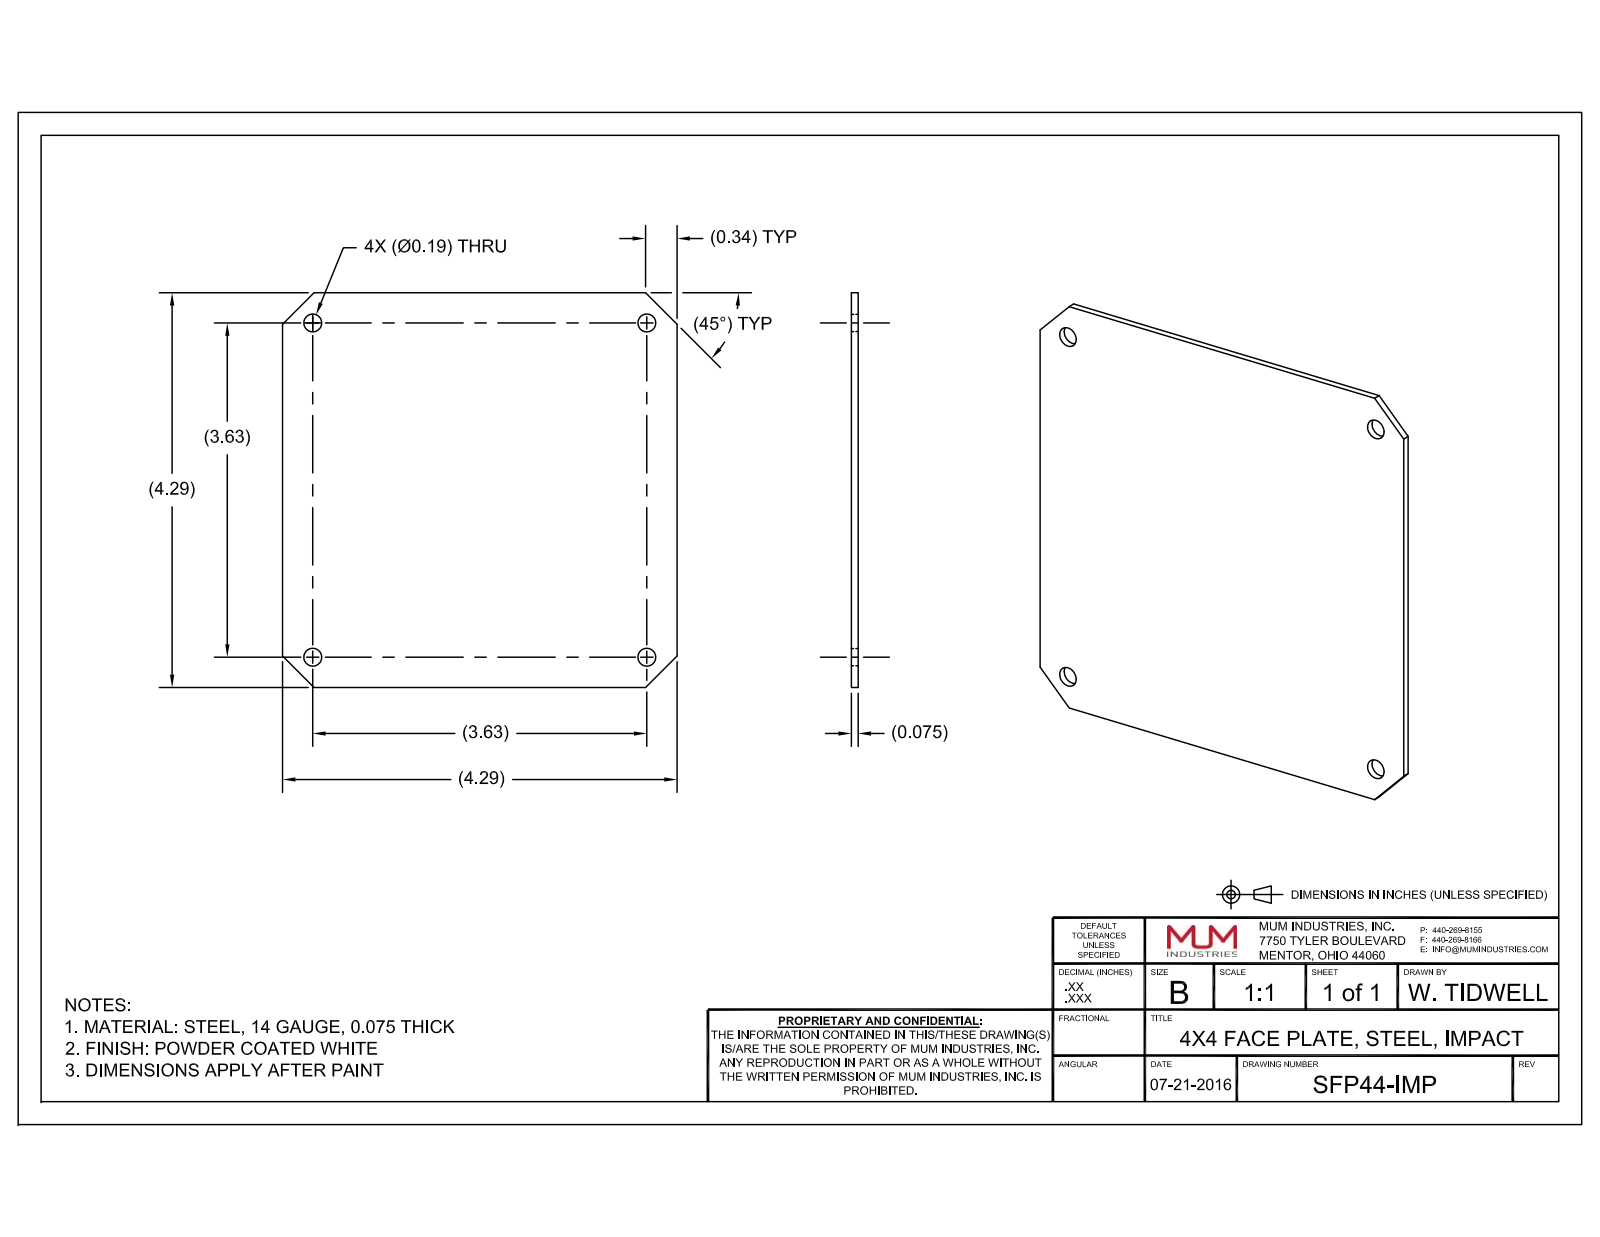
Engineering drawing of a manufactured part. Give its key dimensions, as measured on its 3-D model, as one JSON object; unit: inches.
{"part_name": "SFP44-IMP; SUPPORT-FP-4043; 9912597-82-10; SFPK44-IMP_ASM", "step_written_by": "CREO PARAMETRIC BY PTC INC, 2016050 (CONFIG_CONTROL_DESIGN)", "units": "inches", "bodies": {"solids": 13, "faces": 1578, "planar": 362, "cylindrical": 636, "other": 580}, "overall_size": [4.351, 4.351, 2.47], "volume_in3": 3.167, "surface_area_in2": 76.27, "round_holes": [[0.194, 4]], "round_bosses_or_shafts": [[0.322, 8], [0.164, 8], [0.119, 8]], "partial_cylinders_radius": [[0.01, 100], [0.03, 60], [0.035, 36], [0.046, 20], [0.09, 16], [0.13, 16], [0.06, 12], [0.012, 8]], "face_to_face_distances": [0.075, 0.102, 1.935, 1.86, 2.618, 2.418, 0.2, 0.11, 1.97, 2.045], "hole_center_spacings": [3.632, 5.137]}
